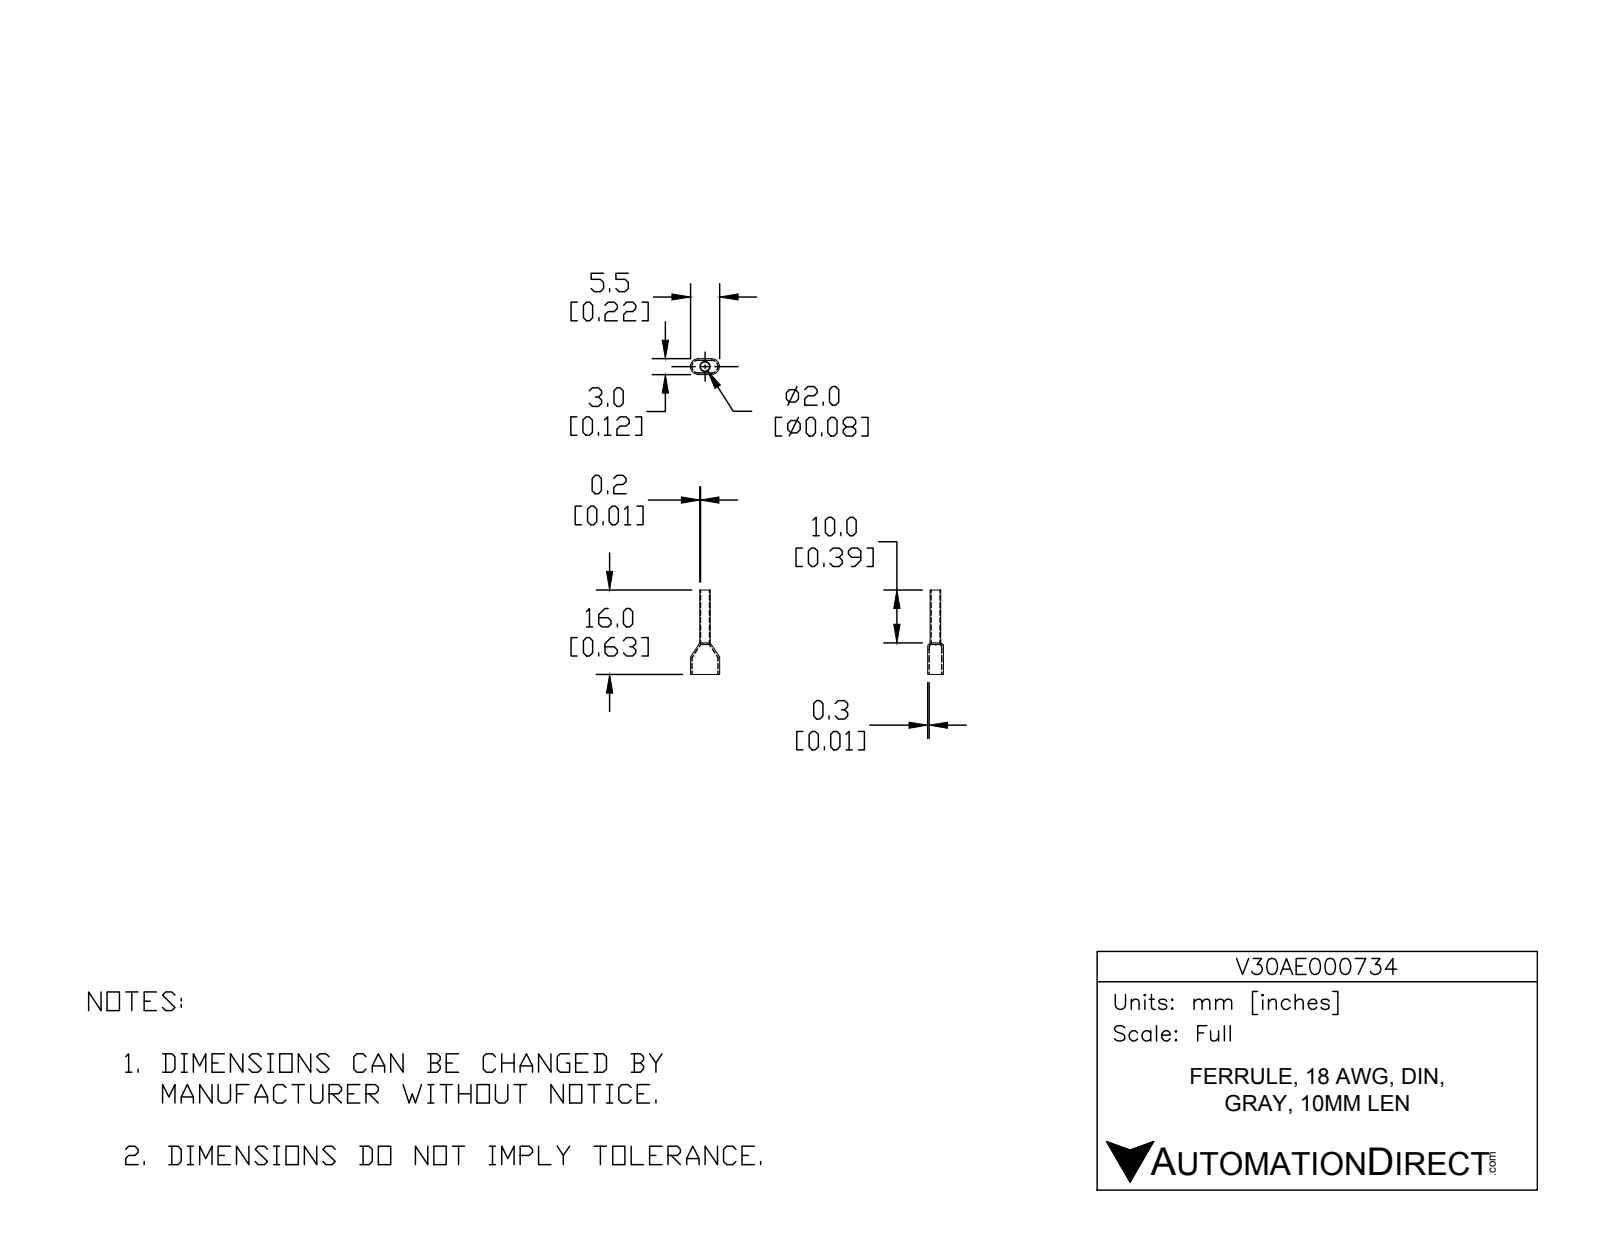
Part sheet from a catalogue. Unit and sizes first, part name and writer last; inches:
Units: inches
Overall size (bounding box): 0.63 × 0.217 × 0.118
Round holes (diameter × count): ⌀0.067 ×1
Round bosses / shafts (diameter × count): ⌀0.079 ×1
Partial cylindrical surfaces — rounded edges, fillets, slot ends (radius × count): R0.047 ×4, R0.059 ×4
Main face-to-face distances: 0.106, 0.118, 0.094, 0.236, 0.63, 0.394, 0.224, 0.406
Volume: 0.002 in³ · Surface area: 0.417 in²
Bodies: 2 solids, 36 faces (14 planar, 22 cylindrical, 0 other)
Part name (STEP PRODUCT): V30AE000734
STEP written by: SolidWorks 2017 (AUTOMOTIVE_DESIGN)
